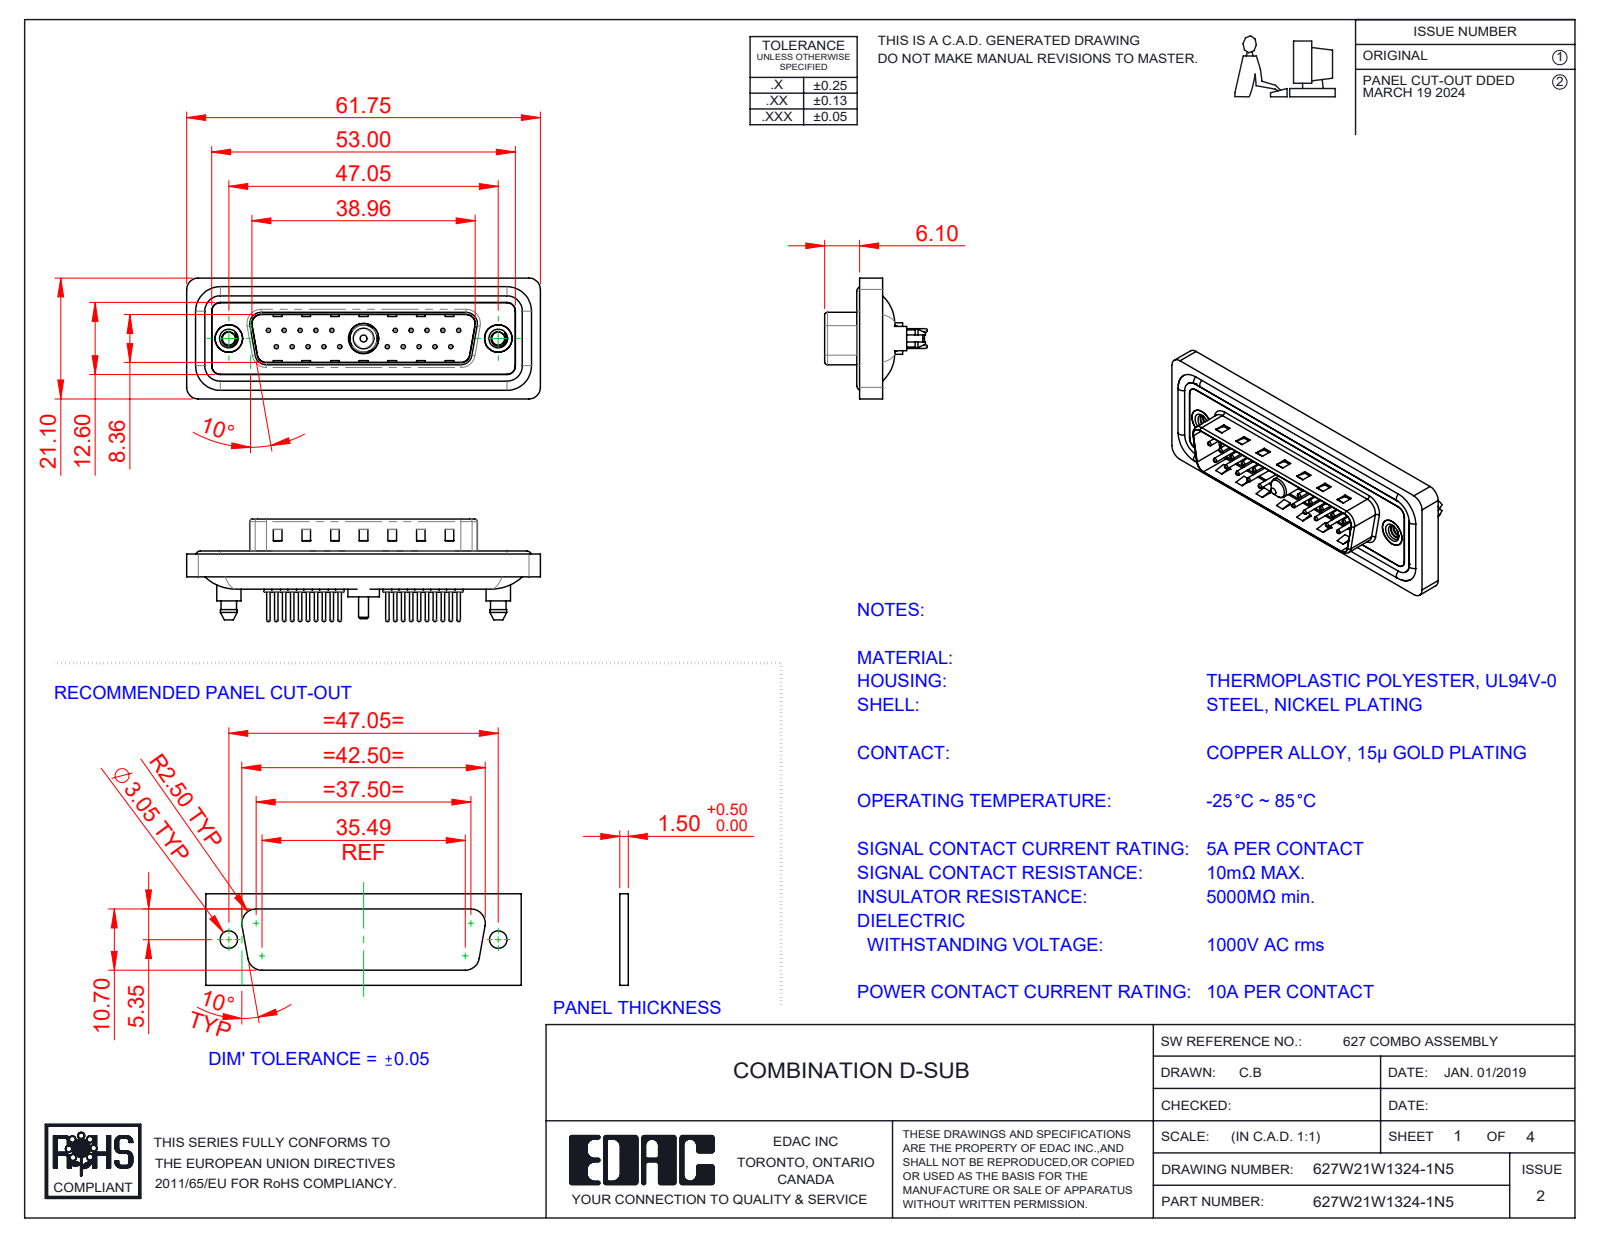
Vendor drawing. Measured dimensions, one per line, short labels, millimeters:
name: 627Combo Contact Row 2_24; Power Pin_10A S; 627Combo Shell Front_25 Contacts; 627Combo Shell Rear_25 Contacts (+5 more)
written by: SolidWorks 2023 (CONFIG_CONTROL_DESIGN)
unit: mm
bodies: 29 solids, 1312 faces (375 planar, 519 cylindrical, 418 other)
size: 61.75 × 21.1 × 17.9
volume: 7 317 mm³; area: 12 274 mm²
holes: 20× ⌀0.75, 20× ⌀1.6, 20× ⌀2, 2× ⌀2.26, 2× ⌀4, 2× ⌀4.8, 2× ⌀5, 1× ⌀4.85, 1× ⌀5.3
bosses: 20× ⌀1.5, 20× ⌀0.6, 4× ⌀1.6, 2× ⌀5.4, 2× ⌀4.9, 2× ⌀4.25, 1× ⌀5.5, 1× ⌀5.2
rounds: 24× R1.5, 18× R2, 10× R1.6, 8× R0.5, 4× R0.25, 4× R0.6, 4× R0.65, 4× R0.9
face distances: 0.4, 1.5, 1.1, 1.6, 0.5, 3.1, 2.9, 4.1, 0.82, 9.58
hole spacings: 3.16, 2.77, 5.54, 8.31, 5.04, 19.39, 20.97, 22.16
